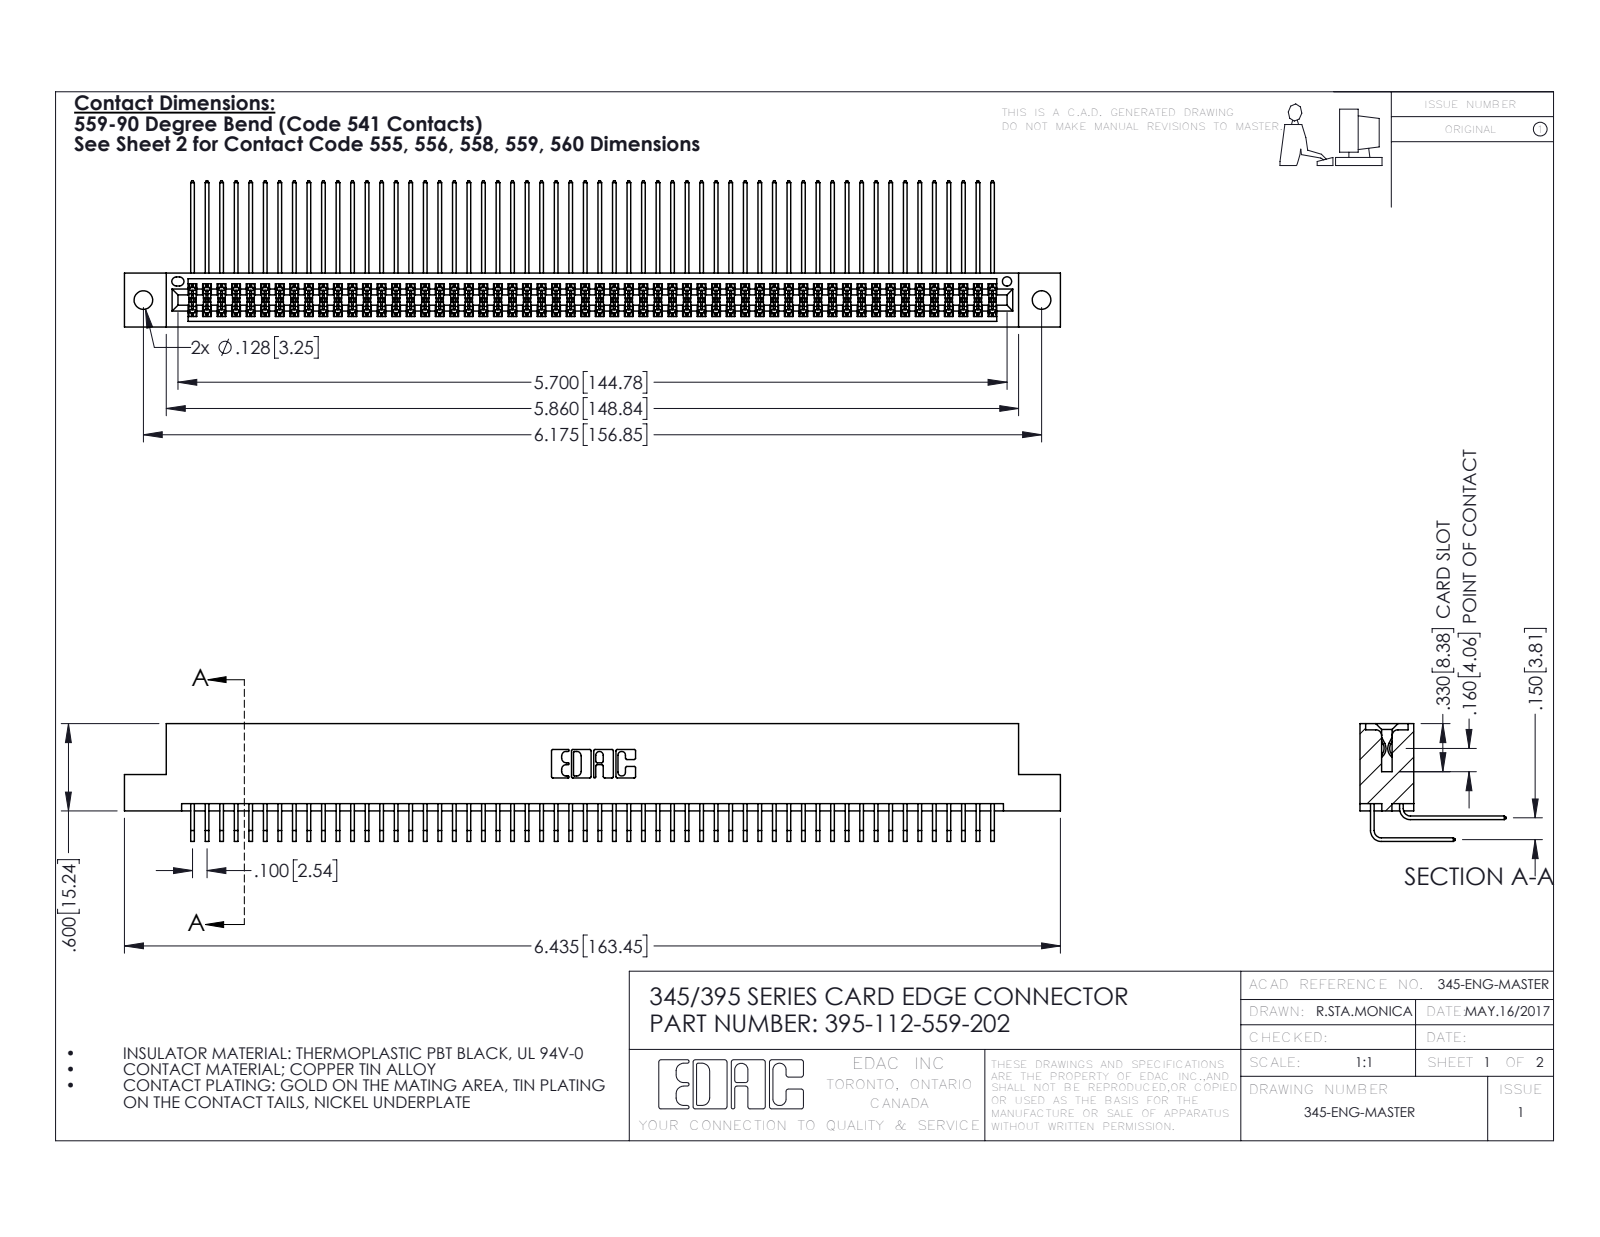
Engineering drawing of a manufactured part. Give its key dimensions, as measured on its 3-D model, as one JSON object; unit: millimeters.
{"part_name": "345-292-001_558 559 Tail - 1; 345 Part_Flush Mounting Lugs - 0.128 Dia; 395-112-559-202; 345-292-001_559 Tail - 2", "step_written_by": "SolidWorks 2016 (CONFIG_CONTROL_DESIGN)", "units": "millimeters", "bodies": {"solids": 113, "faces": 5950, "planar": 4000, "cylindrical": 1950, "other": 0}, "overall_size": [163.4, 25.5, 20.5], "volume_mm3": 16620, "surface_area_mm2": 27600, "round_holes": [[3.3, 2], [1.6, 1]], "partial_cylinders_radius": [[0.2, 169], [0.3, 22], [0.2, 6], [0.8, 6], [0.7, 3], [0.4, 2], [0.5, 2], [0.6, 2]], "face_to_face_distances": [1.8, 7.6, 5.1, 9.4, 2.5, 6.9, 0.6, 5.7, 4.4, 3.8], "hole_center_spacings": [6.9, 150.9, 156.8]}
